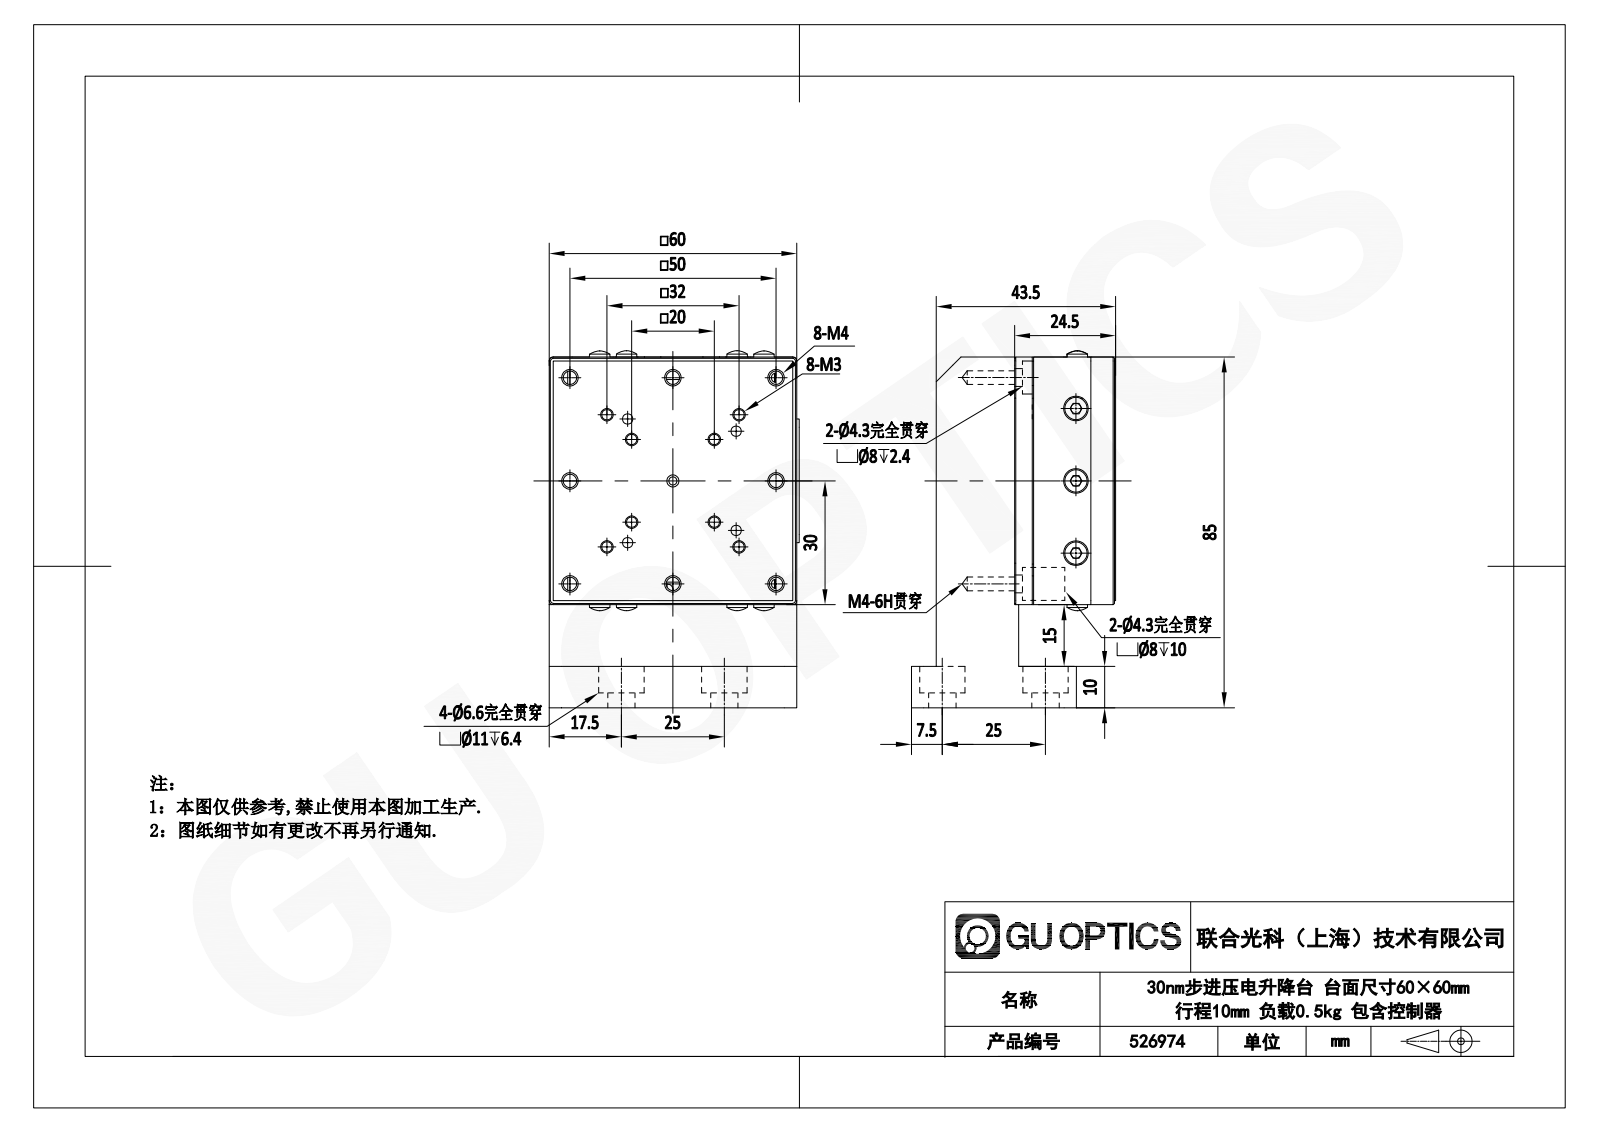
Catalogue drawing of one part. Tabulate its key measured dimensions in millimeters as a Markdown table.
| quantity | value |
| --- | --- |
| part name | 526960 |
| STEP written by | SolidWorks 2020 (CONFIG_CONTROL_DESIGN) |
| units | millimeters |
| bodies | 22 solids, 1149 faces (545 planar, 368 cylindrical, 236 other) |
| overall size | 86.5 × 60.6 × 49.5 |
| volume | 173 409 mm³ |
| surface area | 63 670 mm² |
| round holes (diameter × count) | 2.5 × 39, 4.5 × 16, 1.6 × 15, 3.3 × 12, 2.2 × 7, 3.2 × 5, 4.2 × 5, 4.3 × 4, 6.6 × 4, 8 × 4, 11 × 4, 2.05 × 3 |
| round bosses / shafts (diameter × count) | 5.5 × 5, 3.8 × 5, 3 × 5, 2 × 5 |
| partial cylindrical surfaces (radius × count) | 2 × 26, 1 × 10, 1.5 × 8, 0.3 × 4, 1.9 × 4, 3 × 4, 4 × 3, 2.1 × 2 |
| main face-to-face distances | 10, 60, 24.2, 34.5, 24.5, 13.55, 3.55, 20.95, 10.3, 3.25 |
| hole center spacings | 15, 30, 7, 33.3, 16.53, 16.58, 20, 25 |
